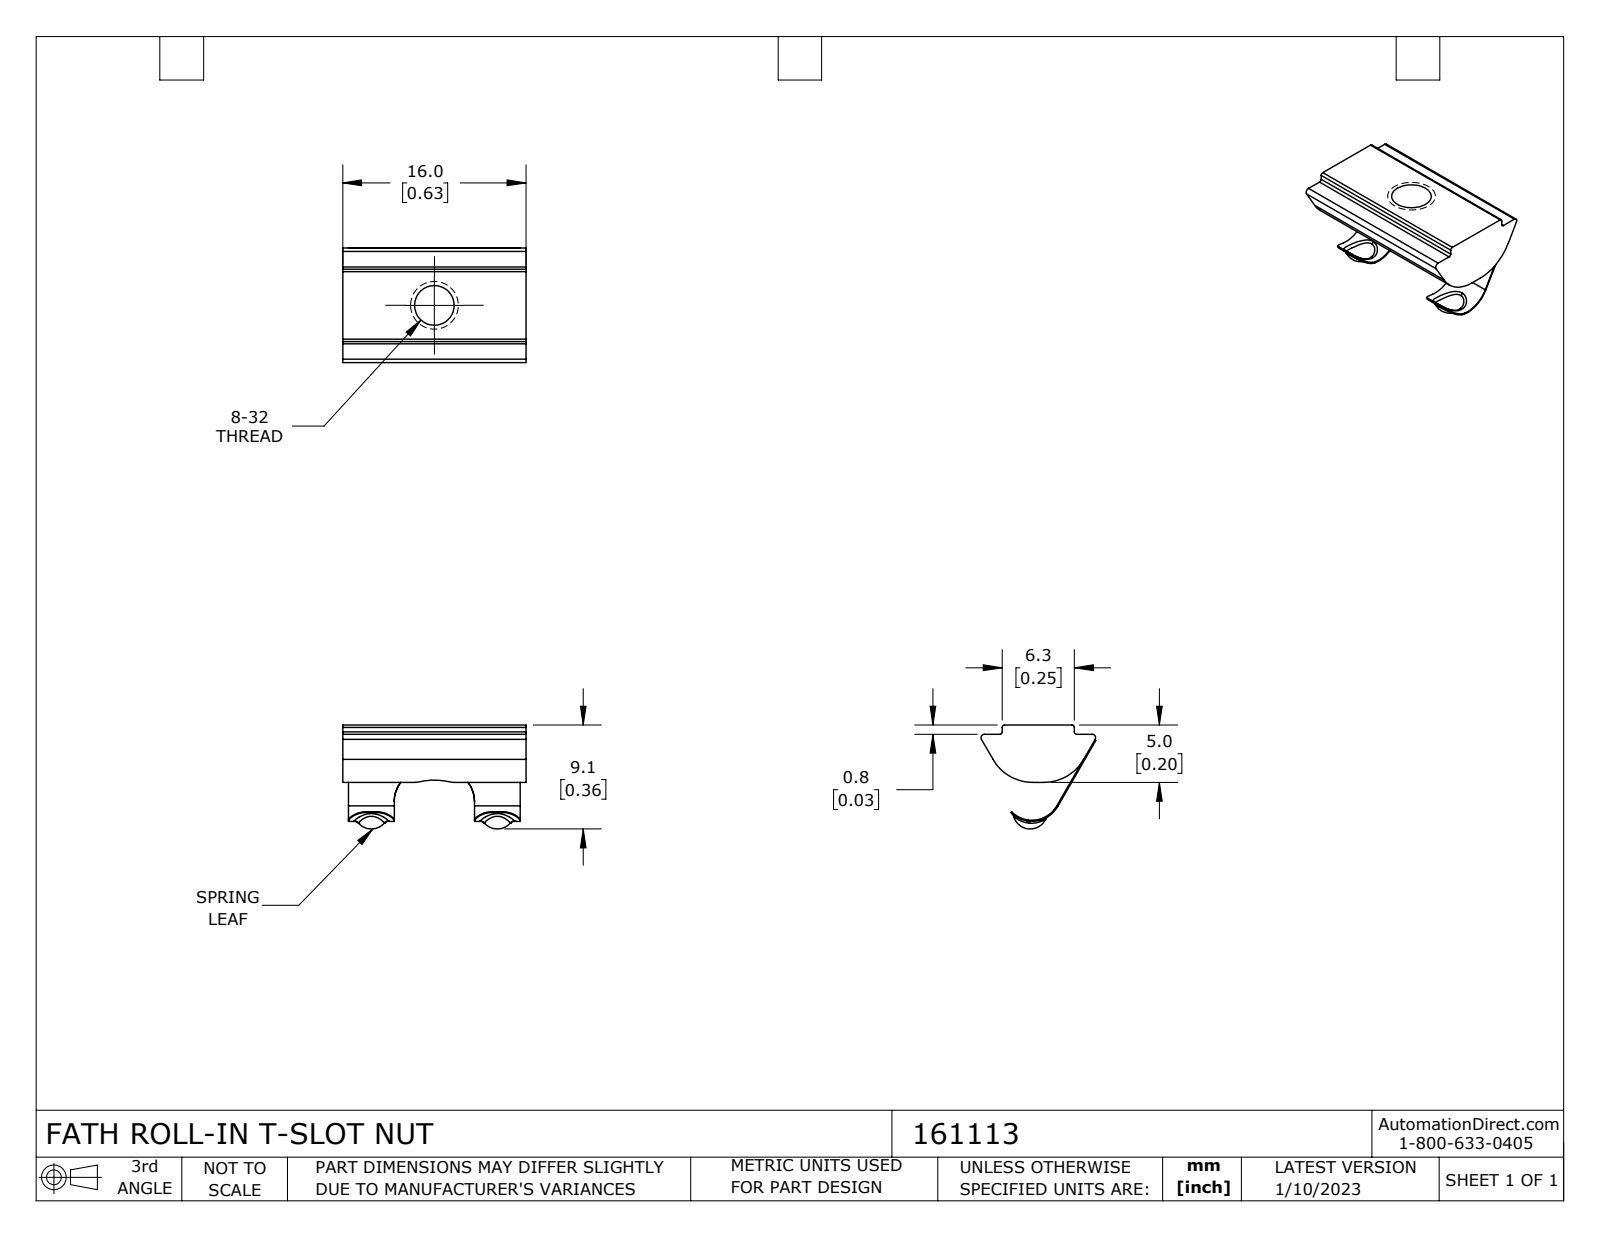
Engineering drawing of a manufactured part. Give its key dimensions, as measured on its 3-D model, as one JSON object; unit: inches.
{"part_name": "161113", "step_written_by": "SolidWorks 2021 (CONFIG_CONTROL_DESIGN)", "units": "inches", "bodies": {"solids": 2, "faces": 57, "planar": 20, "cylindrical": 21, "other": 16}, "overall_size": [0.63, 0.394, 0.357], "volume_in3": 0.034, "surface_area_in2": 1.166, "round_holes": [[0.136, 1]], "partial_cylinders_radius": [[0.008, 4], [0.059, 4], [0.012, 2], [0.157, 2], [0.098, 1], [0.102, 1], [0.138, 1]], "face_to_face_distances": [0.031, 0.63, 0.165, 0.197, 0.248, 0.02, 0.61, 0.591, 0.177, 0.453]}
